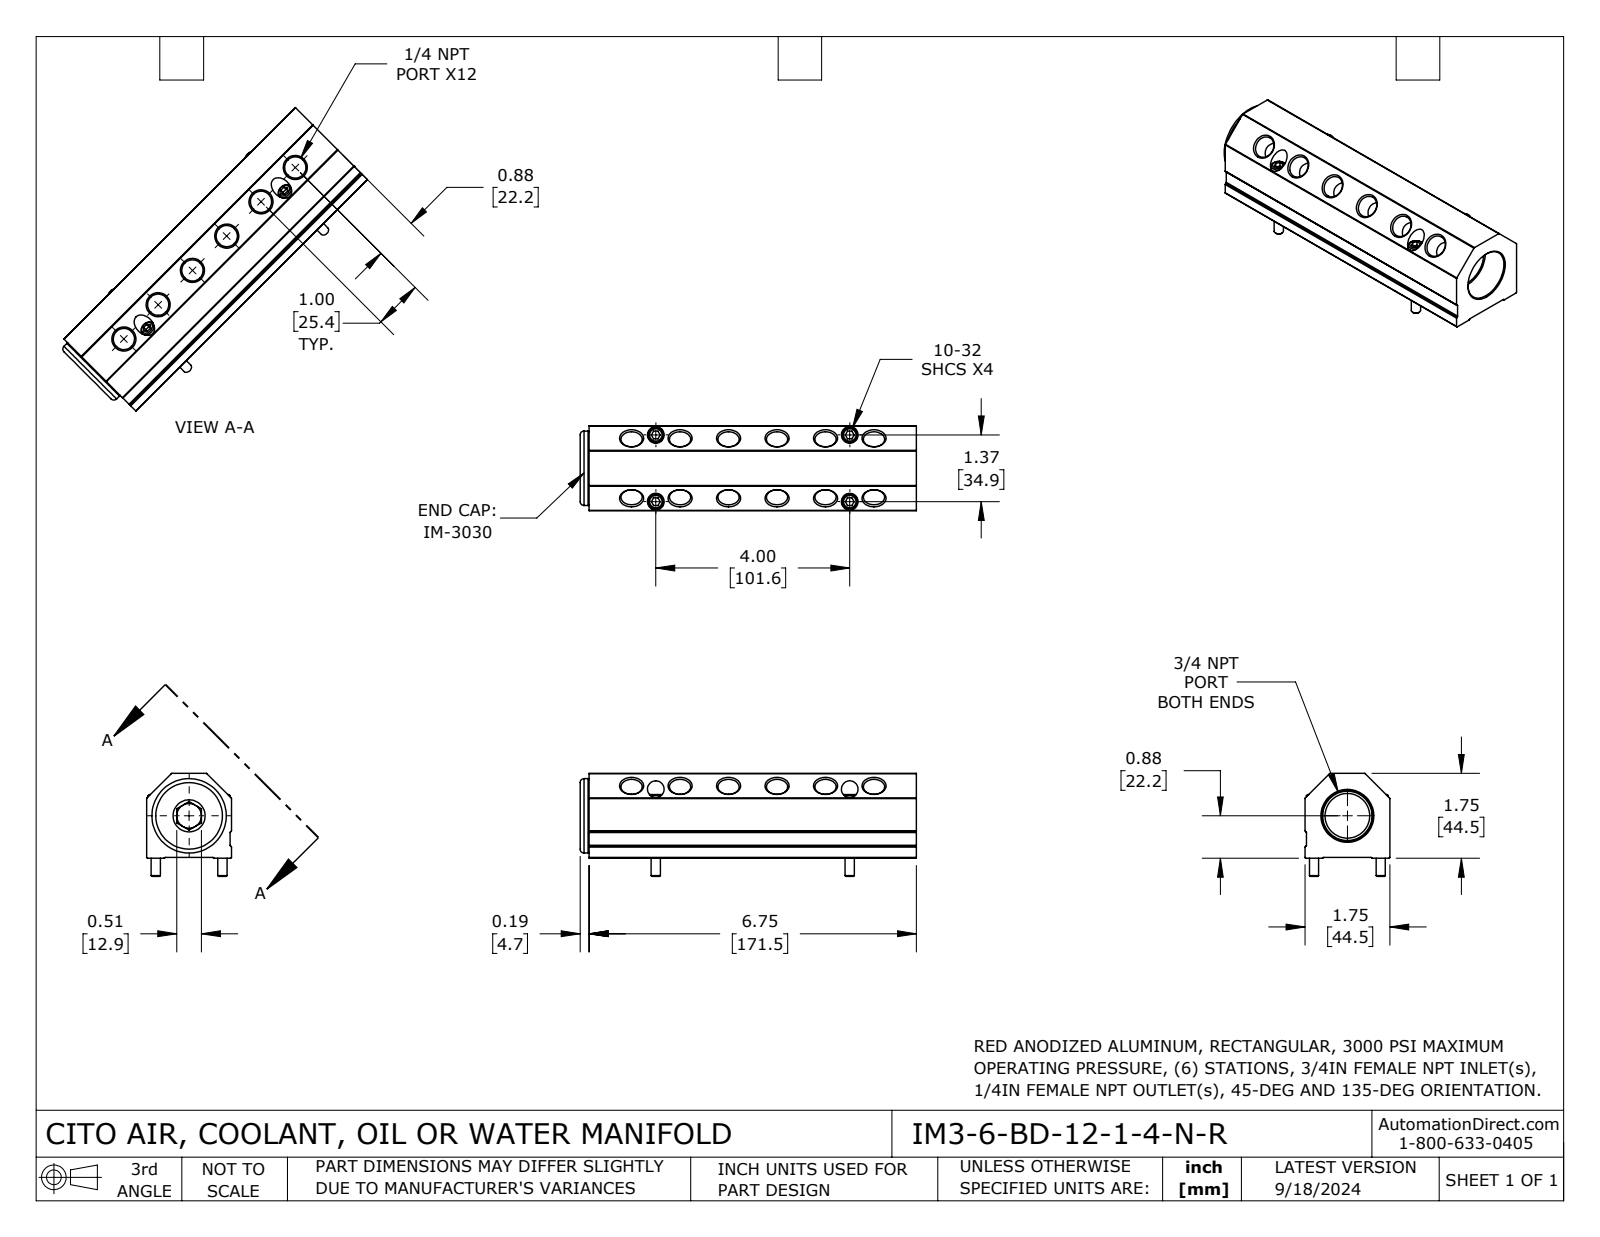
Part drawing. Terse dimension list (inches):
name: IM3-6-BD-12-1-4-N-R
written by: SolidWorks 2023 (CONFIG_CONTROL_DESIGN)
unit: in
bodies: 6 solids, 232 faces (82 planar, 82 cylindrical, 68 other)
size: 6.935 × 2.125 × 1.75
volume: 13.68 in³; area: 86.34 in²
holes: 12× ⌀0.437, 4× ⌀0.203, 4× ⌀0.344, 1× ⌀0.51, 1× ⌀0.921, 1× ⌀1.394
bosses: 4× ⌀0.312, 4× ⌀0.19, 1× ⌀1.534, 1× ⌀1.182, 1× ⌀0.938
rounds: 14× R0.02
face distances: 1.75, 1.73, 0.02, 1.75, 6.75, 0.03, 1.72, 0.185, 6.935, 0.531
hole spacings: 1, 2, 3, 4, 1.375, 4, 4.23, 5
